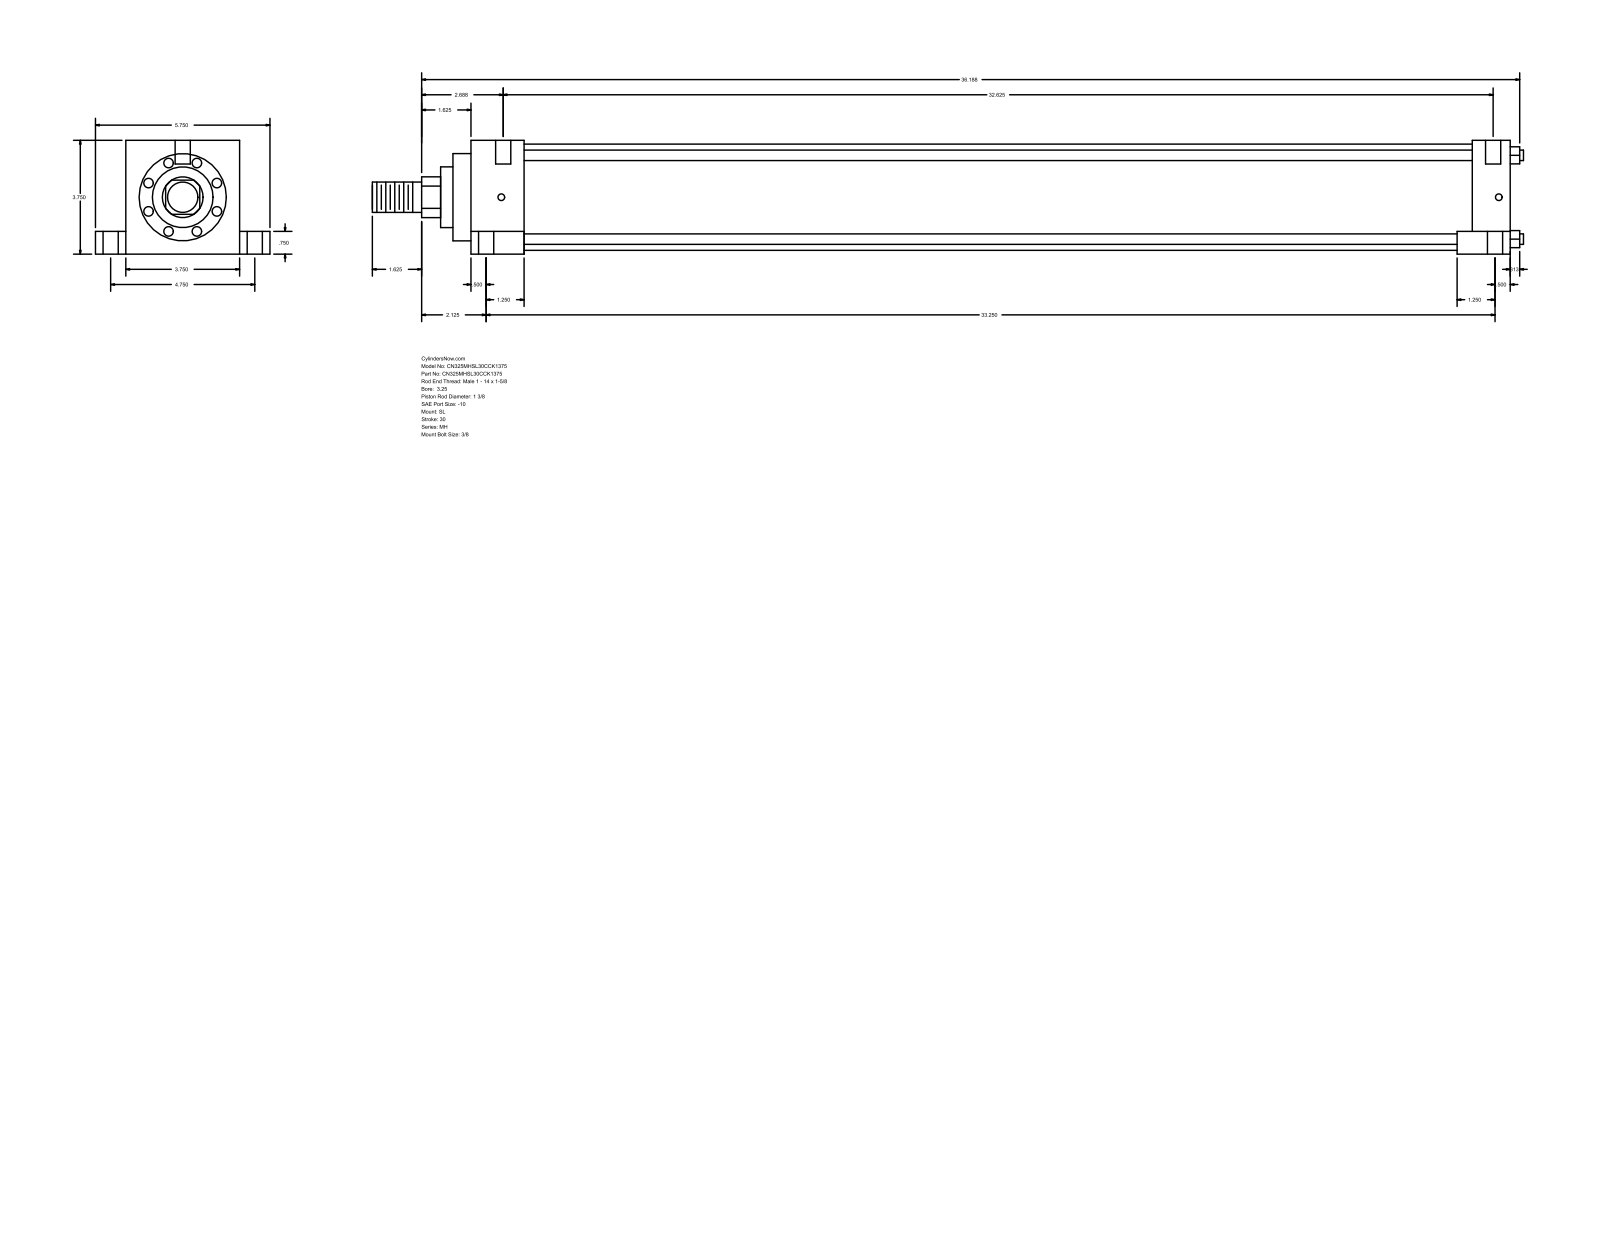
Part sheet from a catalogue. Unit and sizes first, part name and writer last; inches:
Units: inches
Overall size (bounding box): 37.937 × 5.75 × 3.75
Round holes (diameter × count): ⌀0.5 ×6, ⌀0.219 ×4, ⌀0.75 ×4
Round bosses / shafts (diameter × count): ⌀0.345 ×4, ⌀3.5 ×1, ⌀2.875 ×1, ⌀2 ×1, ⌀1.375 ×1, ⌀1 ×1
Partial cylindrical surfaces — rounded edges, fillets, slot ends (radius × count): R0.672 ×1
Main face-to-face distances: 3.75, 34.25, 1.75, 32.5, 1, 4.75, 0.75, 3, 33, 31.25
Hole centre spacings: 2.376, 2.378, 2.427, 2.441, 4.75, 32.774, 32.836, 32.875
Bodies: 0 solids, 110 faces (77 planar, 33 cylindrical, 0 other)
Part name (STEP PRODUCT): MH_SL__0325_1.375
STEP written by: GSSL Pune (CONFIG_CONTROL_DESIGN)
